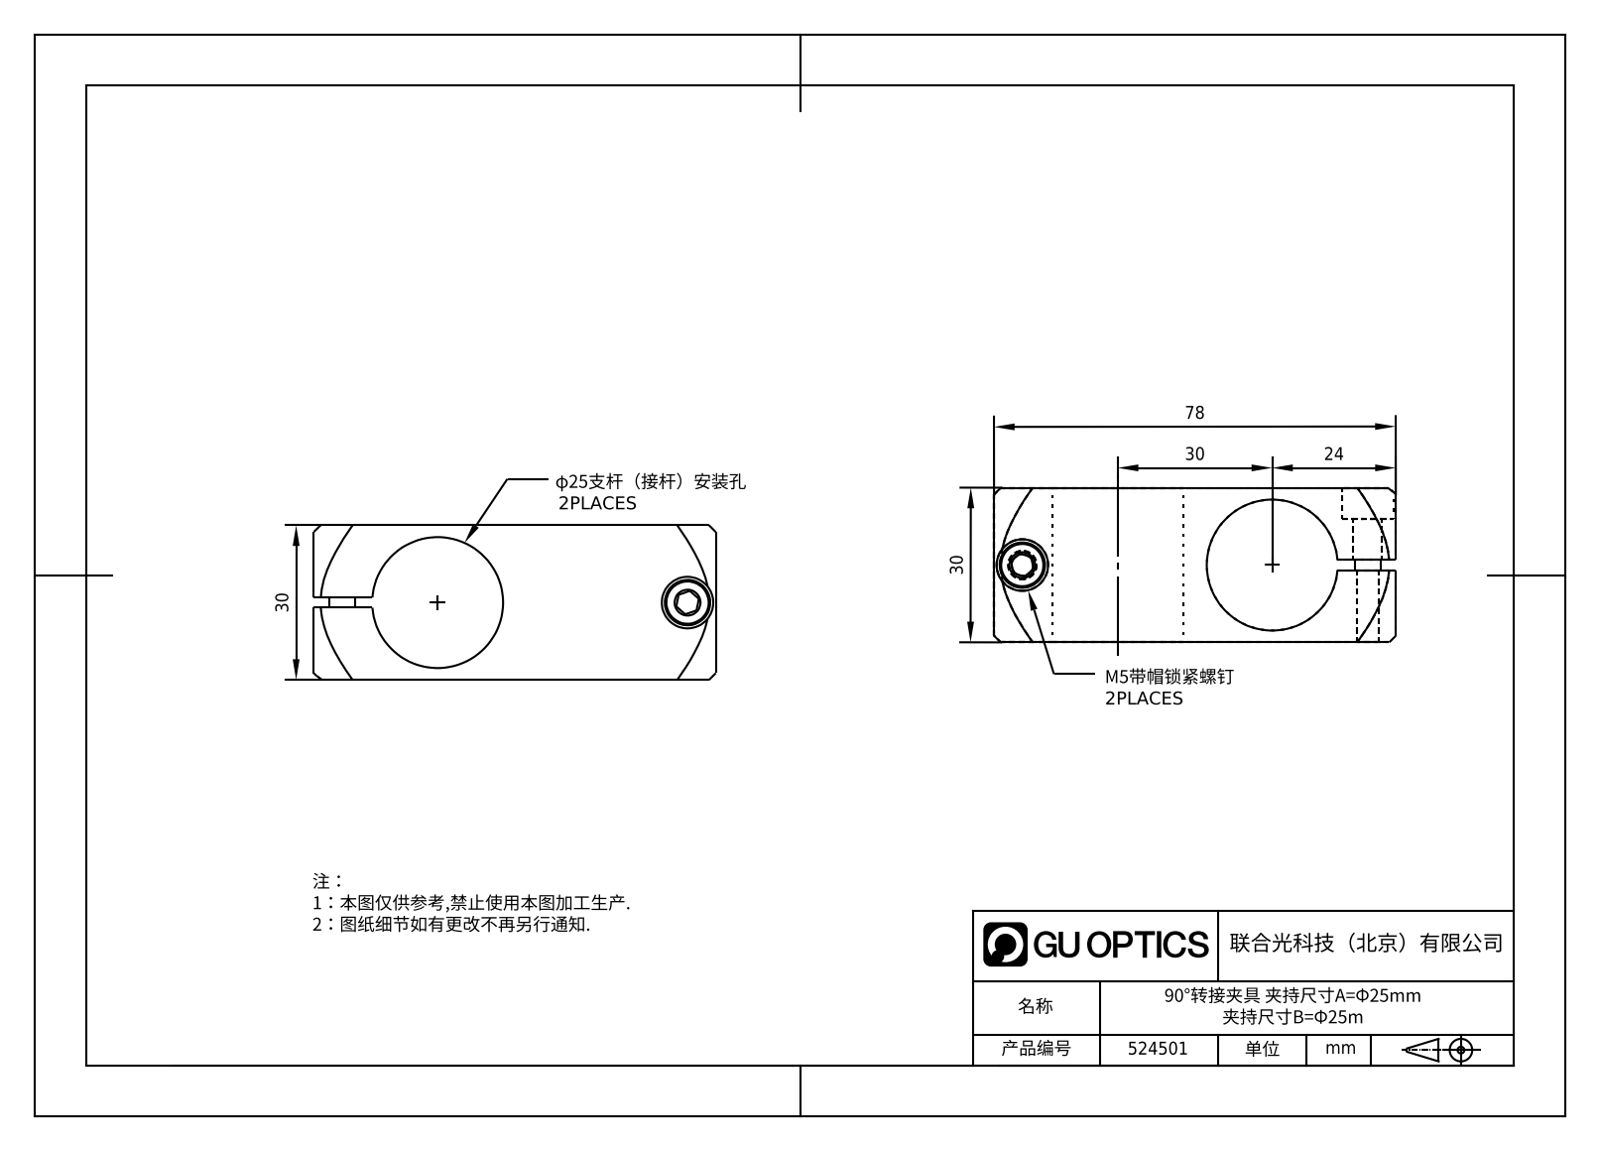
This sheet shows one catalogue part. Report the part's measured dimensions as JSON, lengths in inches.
{"part_name": "1.4.3.36-ZGZ-25Z", "step_written_by": "SolidWorks 2021 (CONFIG_CONTROL_DESIGN)", "units": "inches", "bodies": {"solids": 0, "faces": 57, "planar": 28, "cylindrical": 16, "other": 13}, "overall_size": [3.071, 1.181, 1.181], "round_holes": [[0.165, 2], [0.394, 2], [0.984, 2]], "round_bosses_or_shafts": [[0.346, 2]], "face_to_face_distances": [1.181, 0.551, 0.63, 0.079, 3.071, 0.059, 1.122, 0.571, 0.492, 1.063], "hole_center_spacings": [1.909]}
